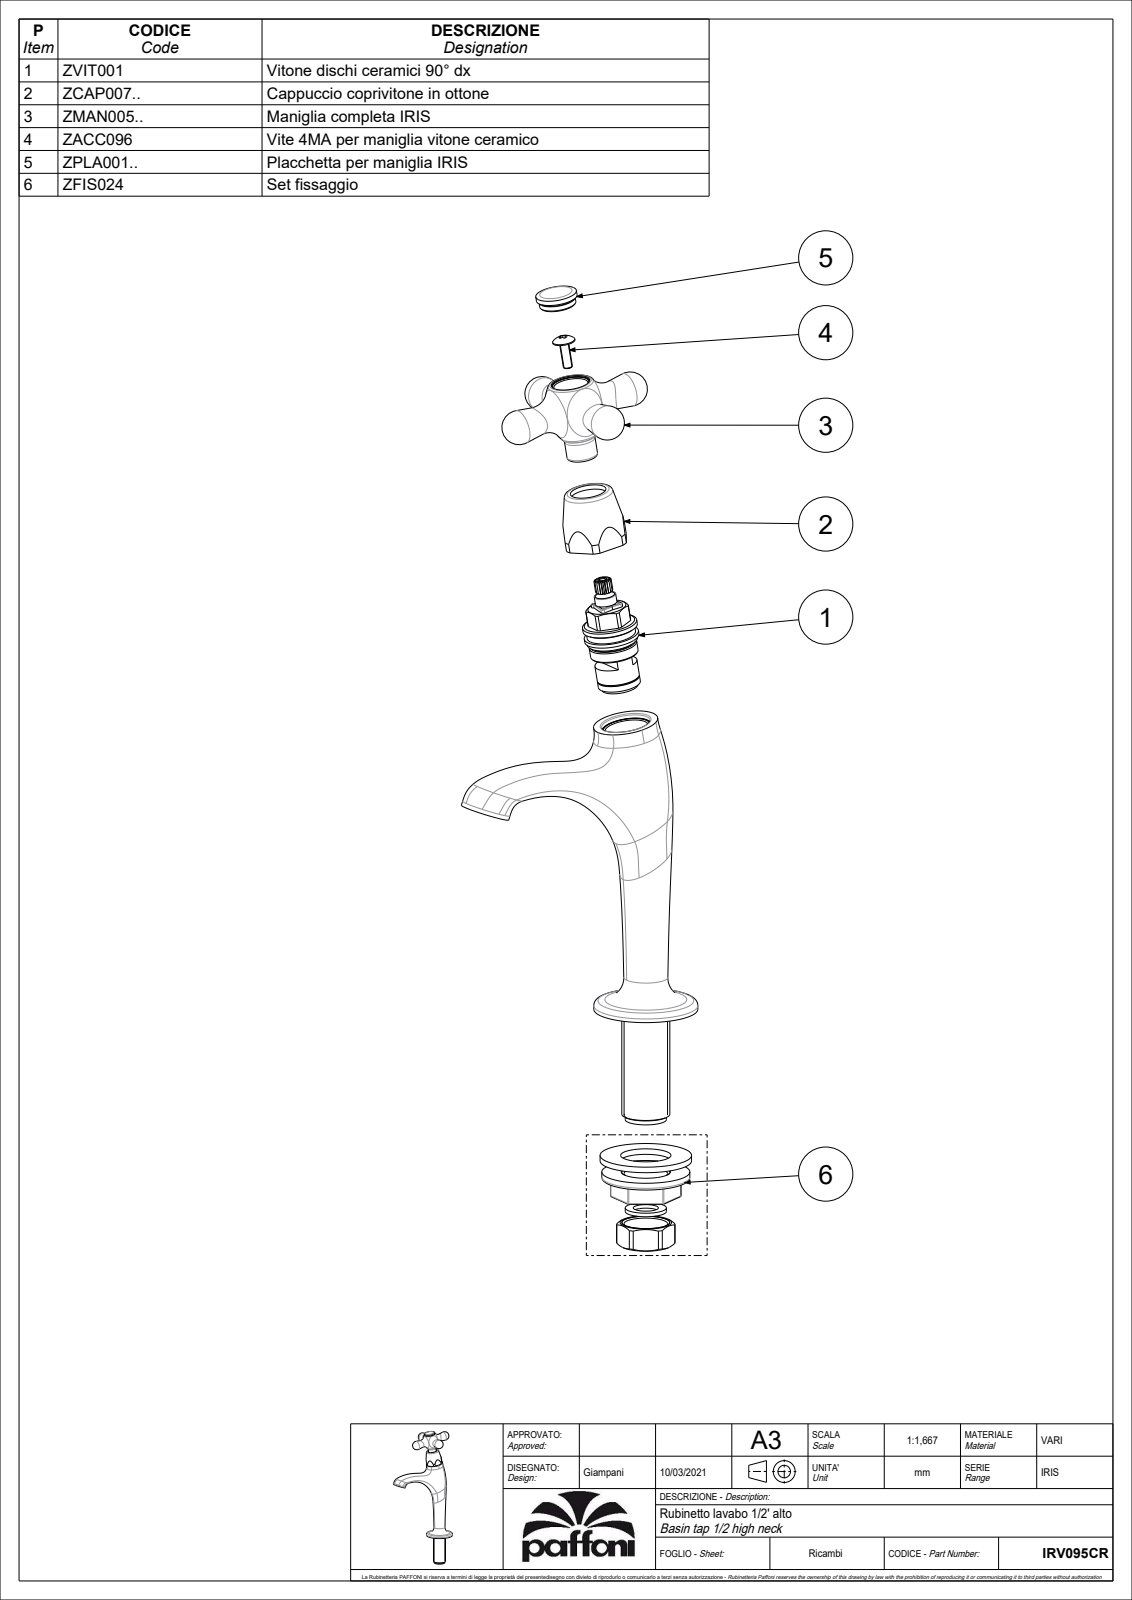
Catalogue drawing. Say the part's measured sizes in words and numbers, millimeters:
The part is named "IRV095CR". Its 3-D file was written by "CREO PARAMETRIC BY PTC INC, 2020044 (CONFIG_CONTROL_DESIGN)". It is 1 solid with 115 faces: 22 planar, 14 cylindrical and 79 other. Overall it measures 189.19 by 114.12 by 72 millimeters. Its volume is 131 857 cubic millimeters and its surface area 25 681 square millimeters. Round bosses or shafts: 1 of diameter 45.5, 1 of diameter 21.7, 1 of diameter 18, 1 of diameter 13.5. Partial cylindrical surfaces (rounded edges, fillets, slot ends): 1 of radius 14.5. The main face-to-face distances are 26.5, 24.01, 55.22, 31.21.
